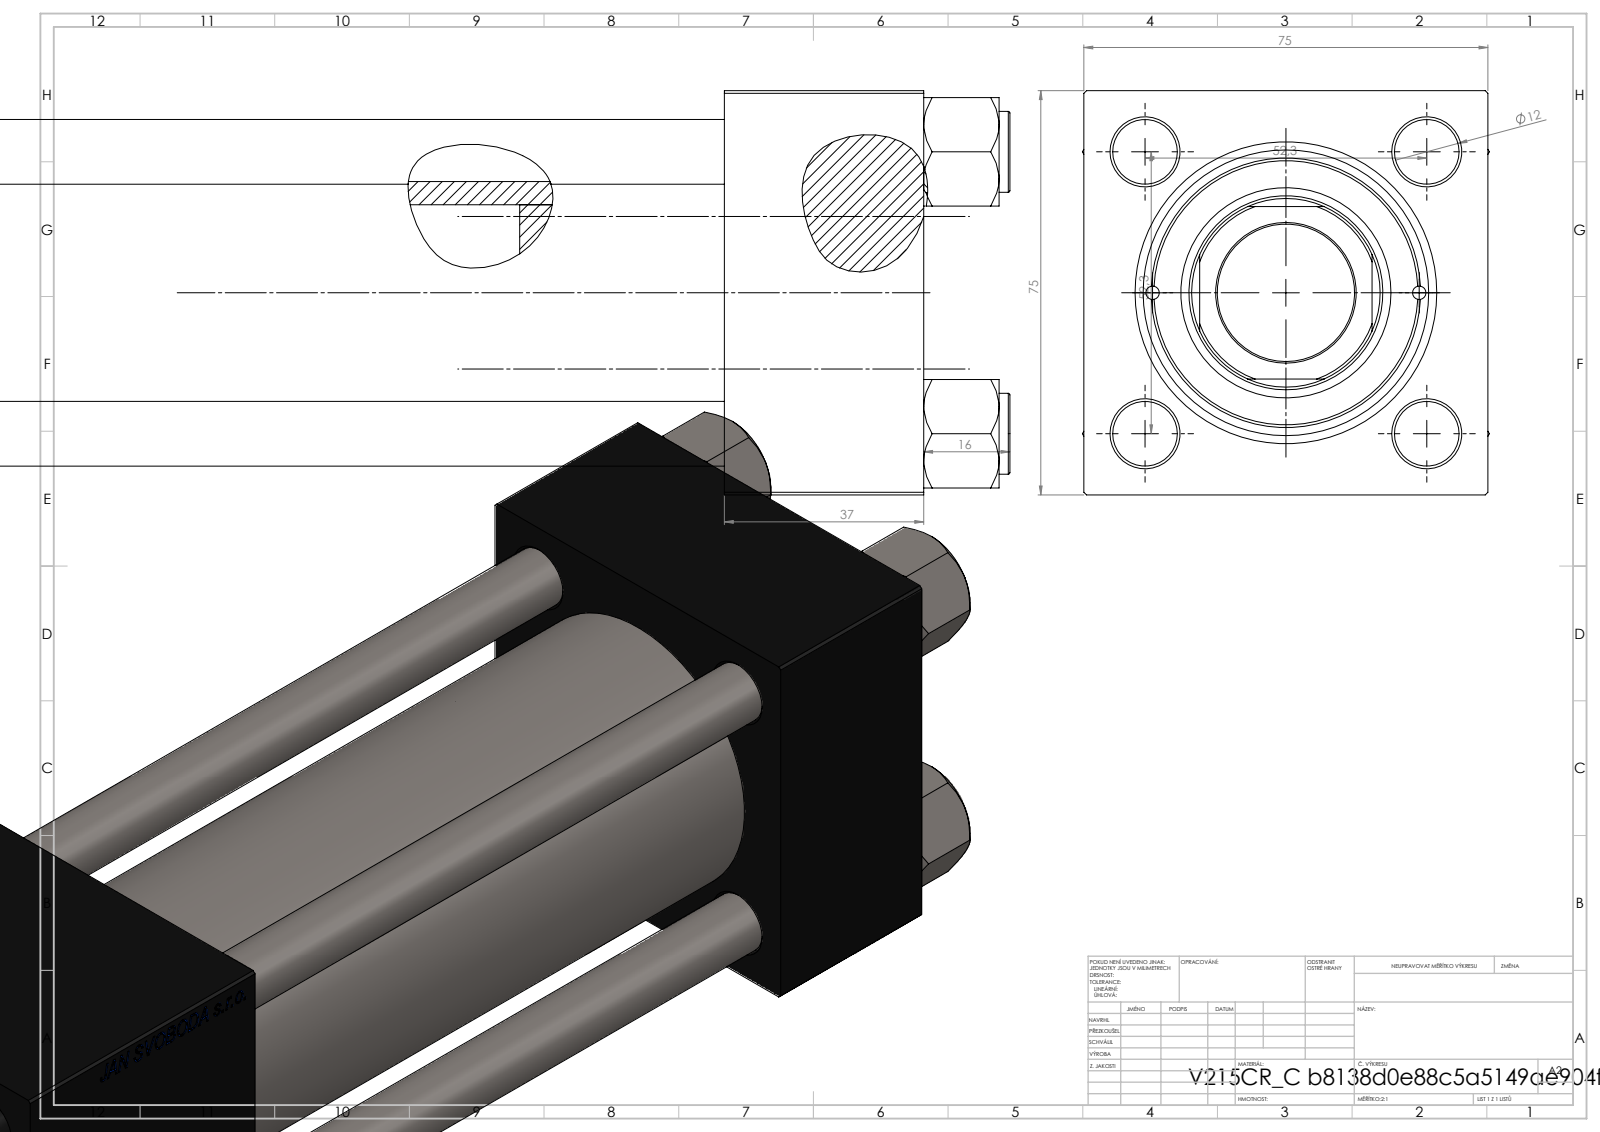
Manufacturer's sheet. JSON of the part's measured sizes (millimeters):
{"part_name": "V215CR_VCP_C; V215CR_C_Body; V215_VC_A; V215CR_C_TYCINKA (+1 more)", "step_written_by": "SolidWorks 2019 (CONFIG_CONTROL_DESIGN)", "units": "millimeters", "bodies": {"solids": 11, "faces": 1154, "planar": 528, "cylindrical": 90, "other": 536}, "overall_size": [275, 75.54, 75], "volume_mm3": 843523, "surface_area_mm2": 203356, "round_holes": [[12, 4], [2.5, 2], [7, 2], [20.96, 2], [30, 2], [25.5, 1], [36, 1], [39, 1], [41, 1], [53, 1]], "round_bosses_or_shafts": [[15, 4], [56, 1], [50, 1]], "partial_cylinders_radius": [[17.5, 1]], "face_to_face_distances": [75, 37, 175, 138, 234, 197, 59, 205.3, 168.3, 30.3], "hole_center_spacings": [26.19, 36.98, 52.3, 57.22, 24.75, 73.96, 49.5, 173.5]}
